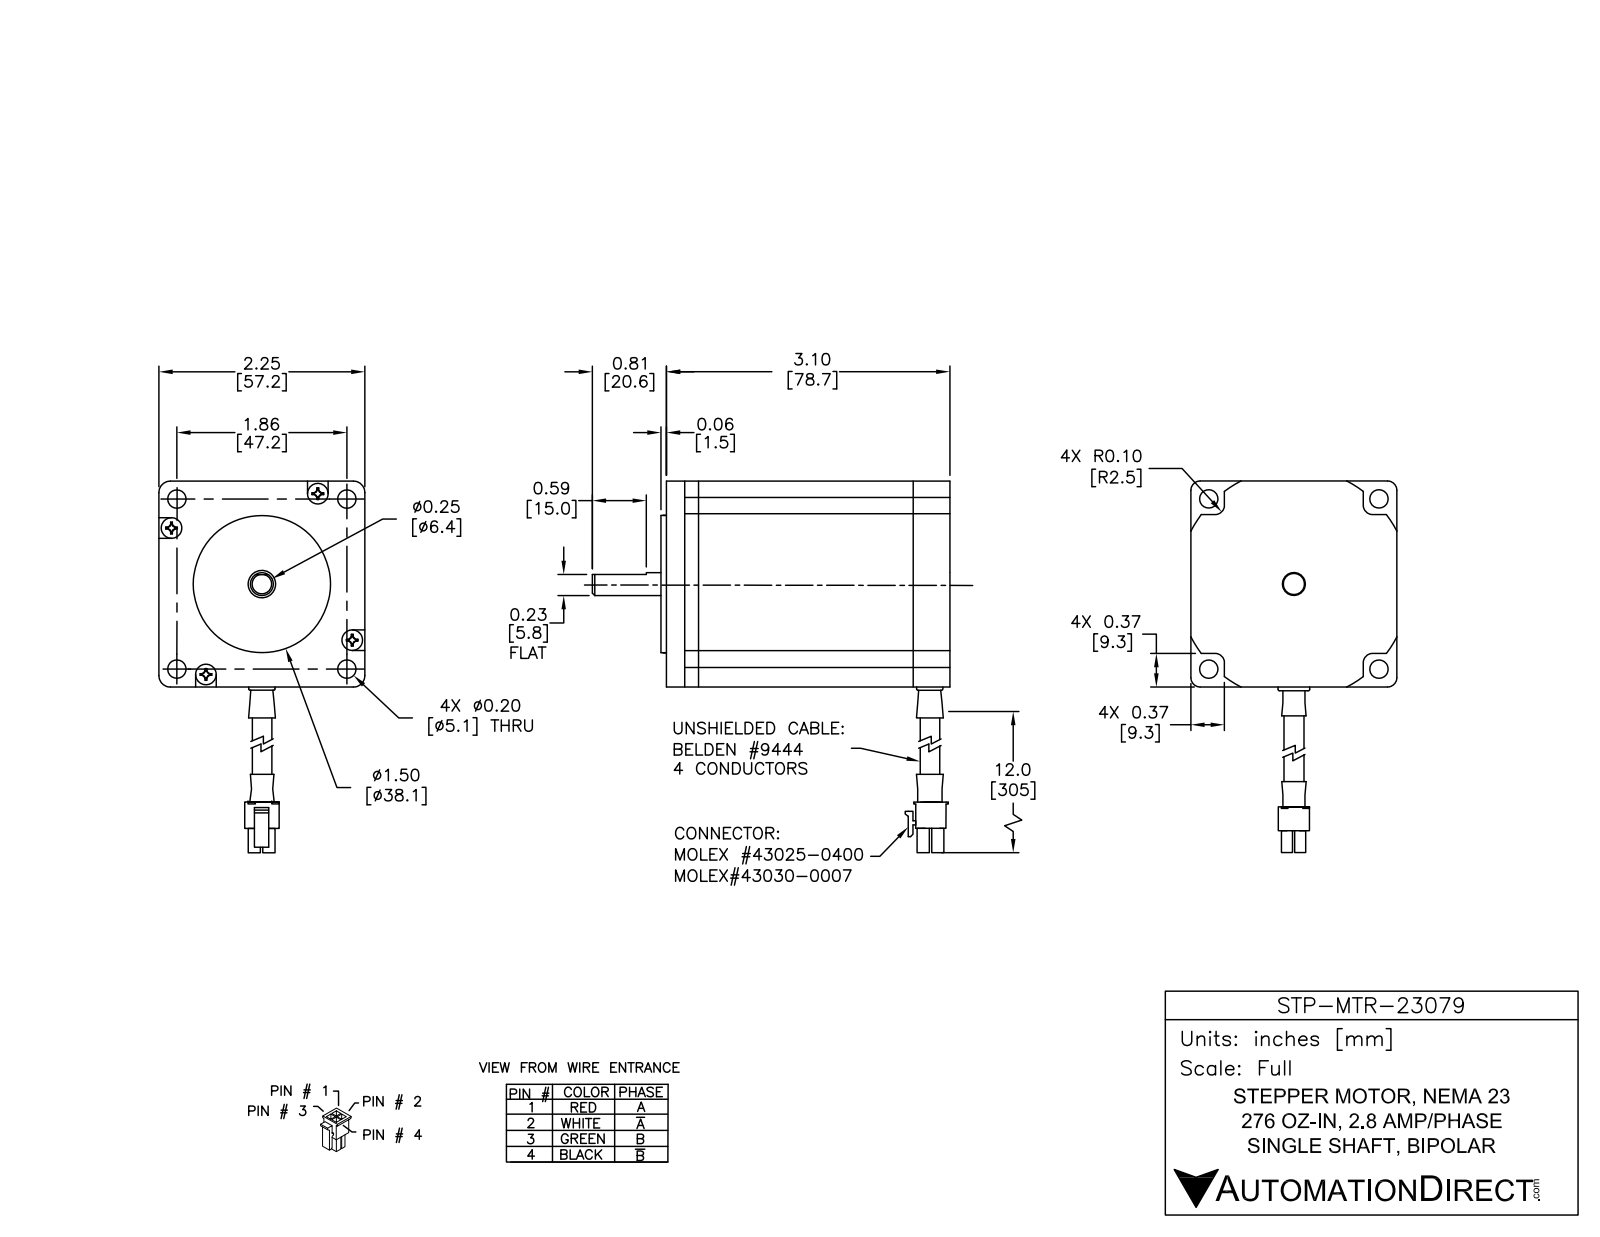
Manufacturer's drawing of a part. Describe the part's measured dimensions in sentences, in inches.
The part is named "STP-MTR-23079". Its 3-D file was written by "SolidWorks 2014 (AUTOMOTIVE_DESIGN)". It is 17 solids with 1915 faces: 838 planar, 956 cylindrical and 121 other. Overall it measures 14.207 by 3.783 by 2.207 inches. Its volume is 9.541 cubic inches and its surface area 140.6 square inches. Round holes: 5 of diameter 0.2, 4 of diameter 0.097, 4 of diameter 0.118, 1 of diameter 0.063, 1 of diameter 0.295, 1 of diameter 0.394, 1 of diameter 0.398, 1 of diameter 0.45, 1 of diameter 0.474, 1 of diameter 0.65, 1 of diameter 0.7, 1 of diameter 0.707. Round bosses or shafts: 8 of diameter 0.125, 4 of diameter 0.205, 4 of diameter 0.126, 4 of diameter 0.05, 1 of diameter 1.5, 1 of diameter 1.44, 1 of diameter 1.375, 1 of diameter 1.372. Partial cylindrical surfaces (rounded edges, fillets, slot ends): 100 of radius 0.025, 46 of radius 0.03, 40 of radius 0.02, 8 of radius 0.012, 8 of radius 0.14, 4 of radius 0.039, 4 of radius 0.125, 4 of radius 0.129. The main face-to-face distances are 2.207, 0.865, 1.065, 0.139, 2.069, 1.93, 0.048, 0.913, 1.113, 1.978. The hole center spacings are 0.315, 0.316, 1.159, 1.16, 1.236, 1.314, 1.548, 1.548.
